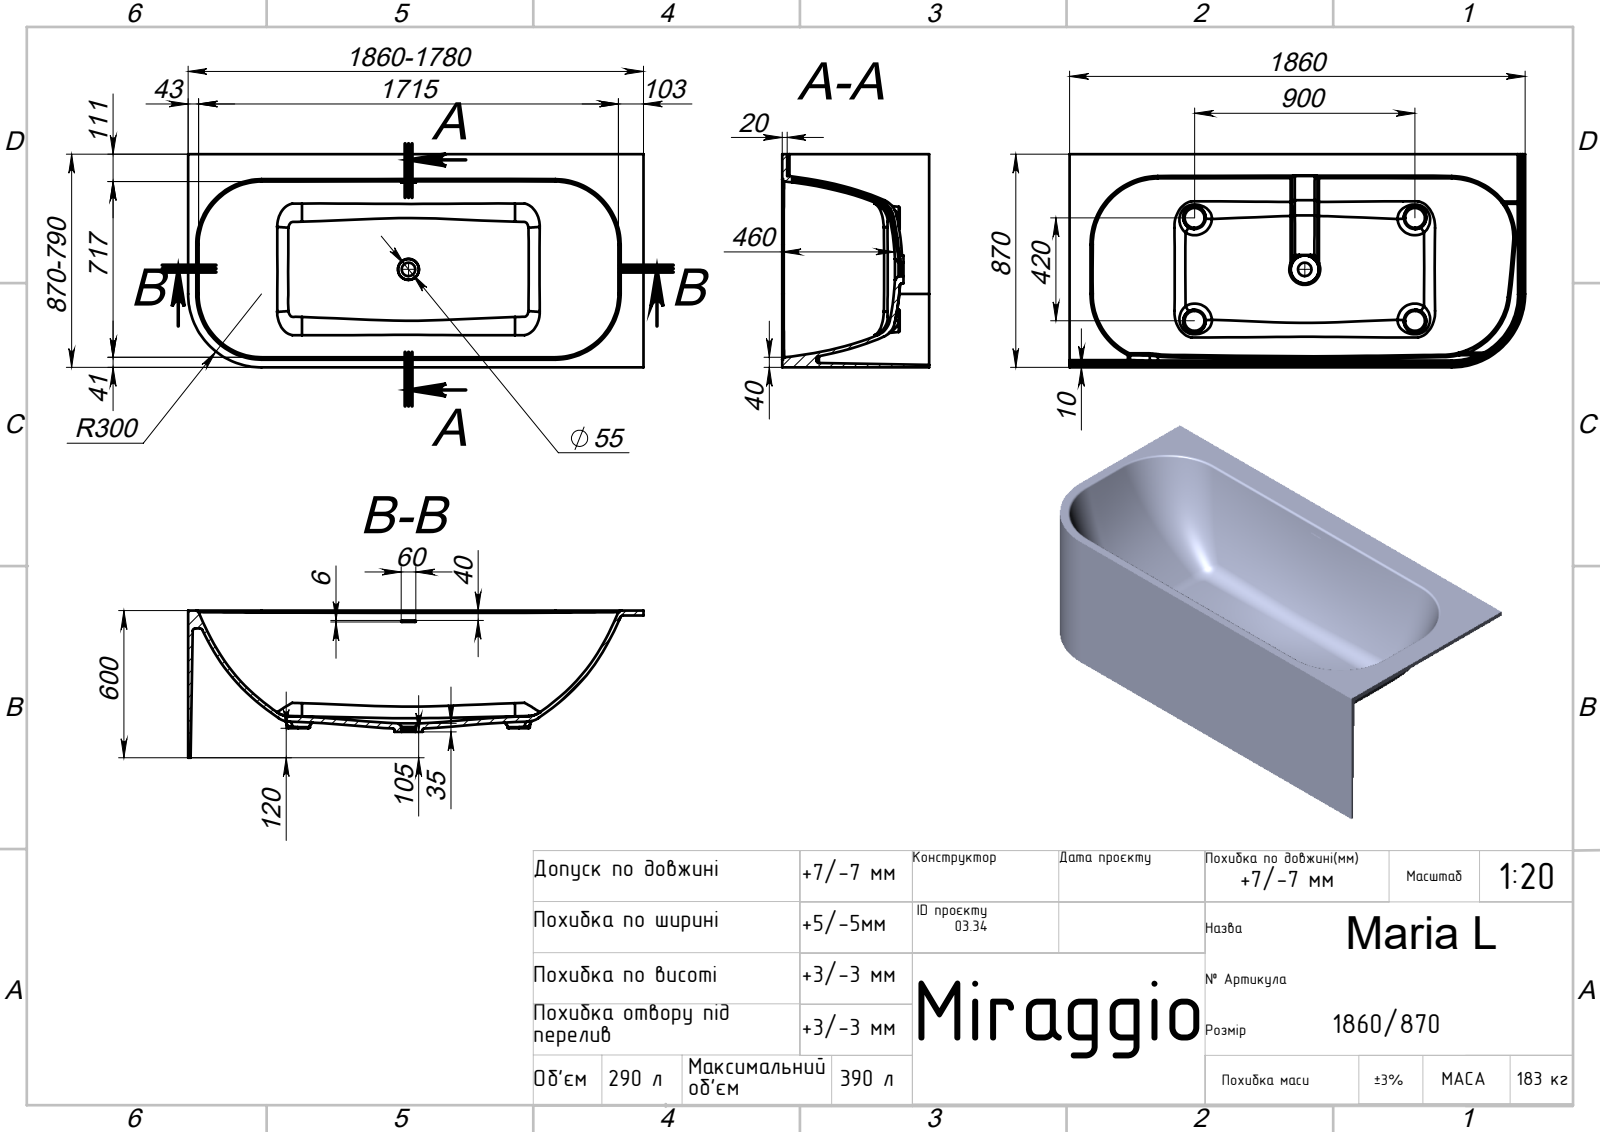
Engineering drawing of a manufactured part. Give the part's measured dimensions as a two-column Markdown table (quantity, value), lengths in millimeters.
| quantity | value |
| --- | --- |
| part name | Maria |
| STEP written by | SolidWorks 2020 (AUTOMOTIVE_DESIGN) |
| units | millimeters |
| bodies | 1 solid, 158 faces (29 planar, 22 cylindrical, 107 other) |
| overall size | 1860 × 870 × 600 |
| volume | 75 530 000 mm³ |
| surface area | 8 323 000 mm² |
| round holes (diameter × count) | 55 × 1 |
| partial cylindrical surfaces (radius × count) | 10 × 5, 50 × 3, 3 × 2, 88 × 1, 90 × 1, 97 × 1, 300 × 1, 2188.55 × 1 |
| main face-to-face distances | 20, 870, 1860, 580, 600, 140, 460, 120, 930, 105 |
